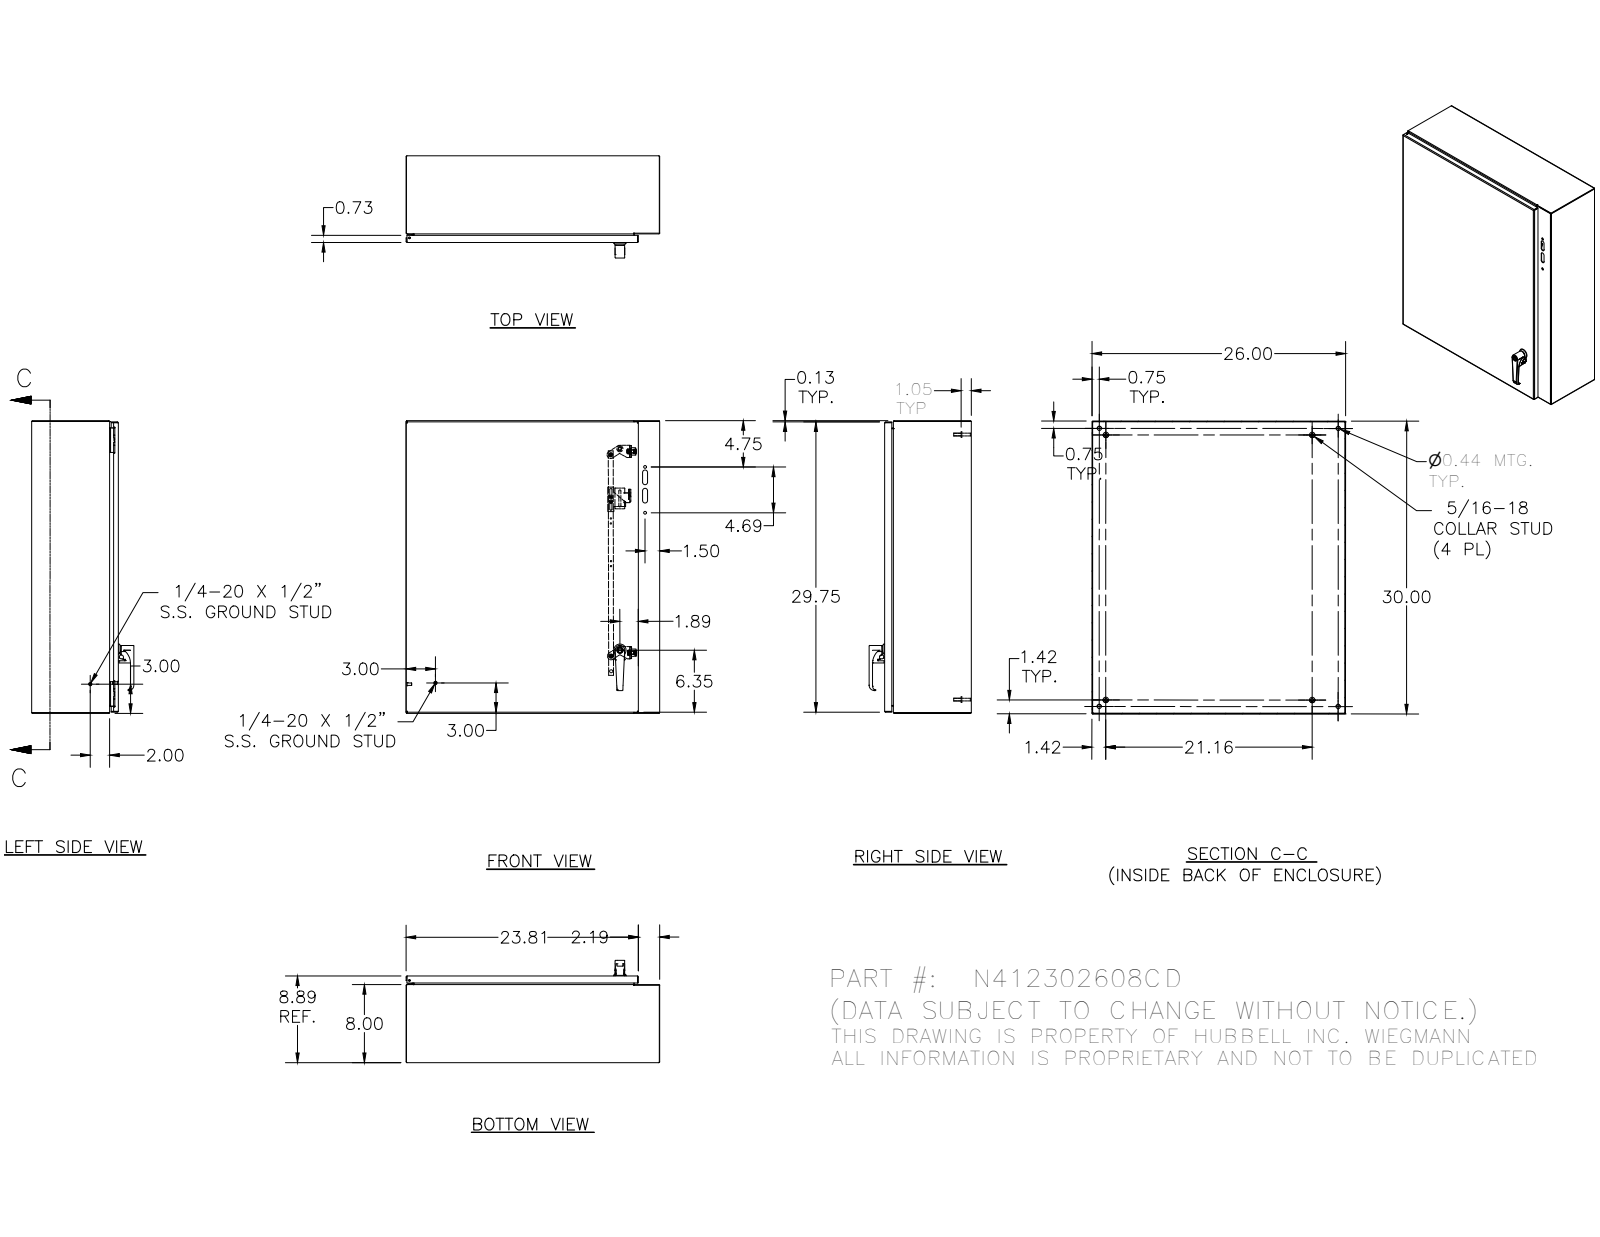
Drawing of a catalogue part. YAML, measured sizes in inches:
part_name: "N412302608CD"
step_written_by: "SolidWorks 2019 (AUTOMOTIVE_DESIGN)"
units: inches
bodies: {solids: 60, faces: 2072, planar: 812, cylindrical: 742, other: 518}
overall_size: [30, 26, 10.512]
volume: 203.7
surface_area: 5453
round_holes:
  - {diameter: 0.145, count: 6}
  - {diameter: 0.093, count: 4}
  - {diameter: 0.152, count: 4}
  - {diameter: 0.156, count: 4}
  - {diameter: 0.167, count: 4}
  - {diameter: 0.172, count: 4}
  - {diameter: 0.187, count: 4}
  - {diameter: 0.437, count: 4}
  - {diameter: 0.32, count: 3}
  - {diameter: 0.196, count: 2}
  - {diameter: 0.211, count: 2}
  - {diameter: 0.22, count: 2}
round_bosses_or_shafts:
  - {diameter: 0.25, count: 12}
  - {diameter: 0.3, count: 8}
  - {diameter: 0.563, count: 4}
  - {diameter: 0.437, count: 4}
  - {diameter: 0.36, count: 4}
  - {diameter: 0.32, count: 4}
  - {diameter: 0.275, count: 4}
  - {diameter: 0.256, count: 4}
partial_cylinders:
  - {radius: 0.02, count: 38}
  - {radius: 0.012, count: 30}
  - {radius: 0.05, count: 26}
  - {radius: 0.125, count: 25}
  - {radius: 0.016, count: 18}
  - {radius: 0.016, count: 16}
  - {radius: 0.025, count: 16}
  - {radius: 0.09, count: 16}
face_to_face_distances: [0.074, 8.843, 8.769, 8.917, 25.926, 29.926, 0.917, 7.926, 26, 25.852]
hole_center_spacings: [26, 0.5, 20.9, 20.9, 24.9, 0.656, 0.66, 0.984]
